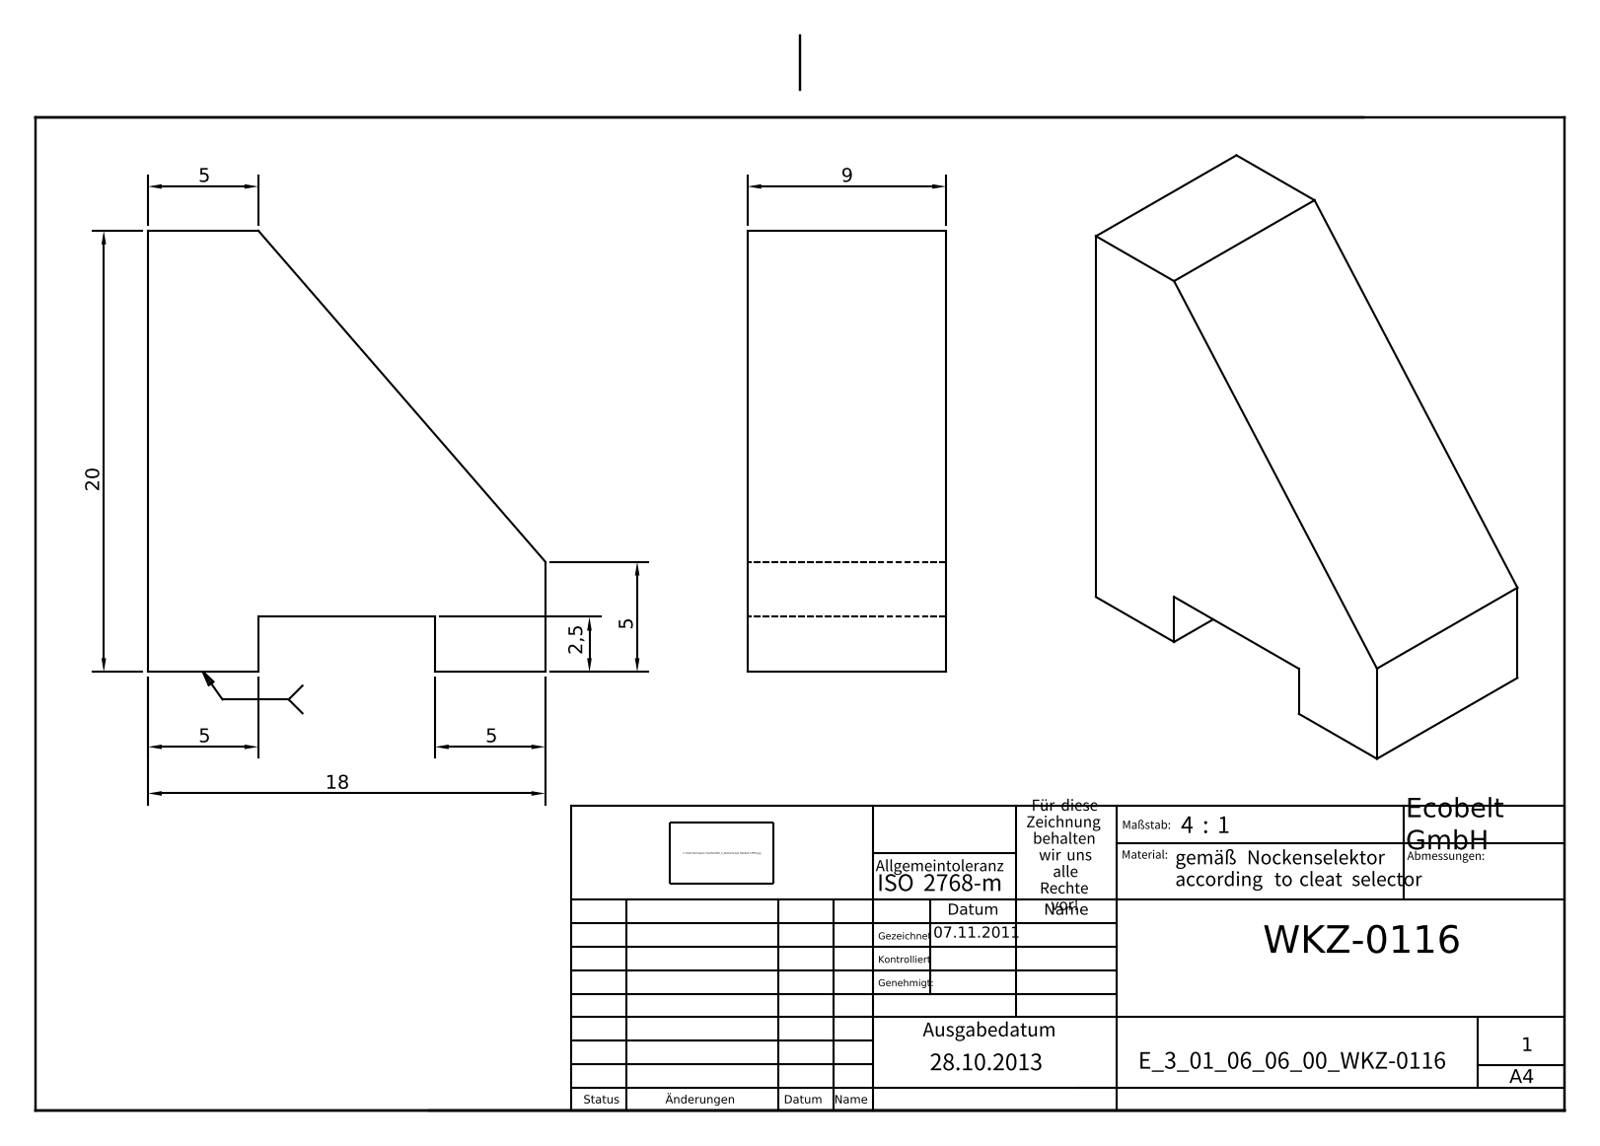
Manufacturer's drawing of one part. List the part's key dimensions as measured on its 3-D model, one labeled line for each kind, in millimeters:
Part name (STEP PRODUCT): E_3_01_06_06_00_WKZ-0116
STEP written by: Autodesk Inventor 2025 (AUTOMOTIVE_DESIGN)
Units: millimetres
Bodies: 1 solid, 11 faces (11 planar, 0 cylindrical, 0 other)
Overall size (bounding box): 20 × 18 × 9
Volume: 2 182 mm³ · Surface area: 1 141 mm²
Main face-to-face distances: 9, 2.5, 18, 20, 17.5, 5, 13, 8
